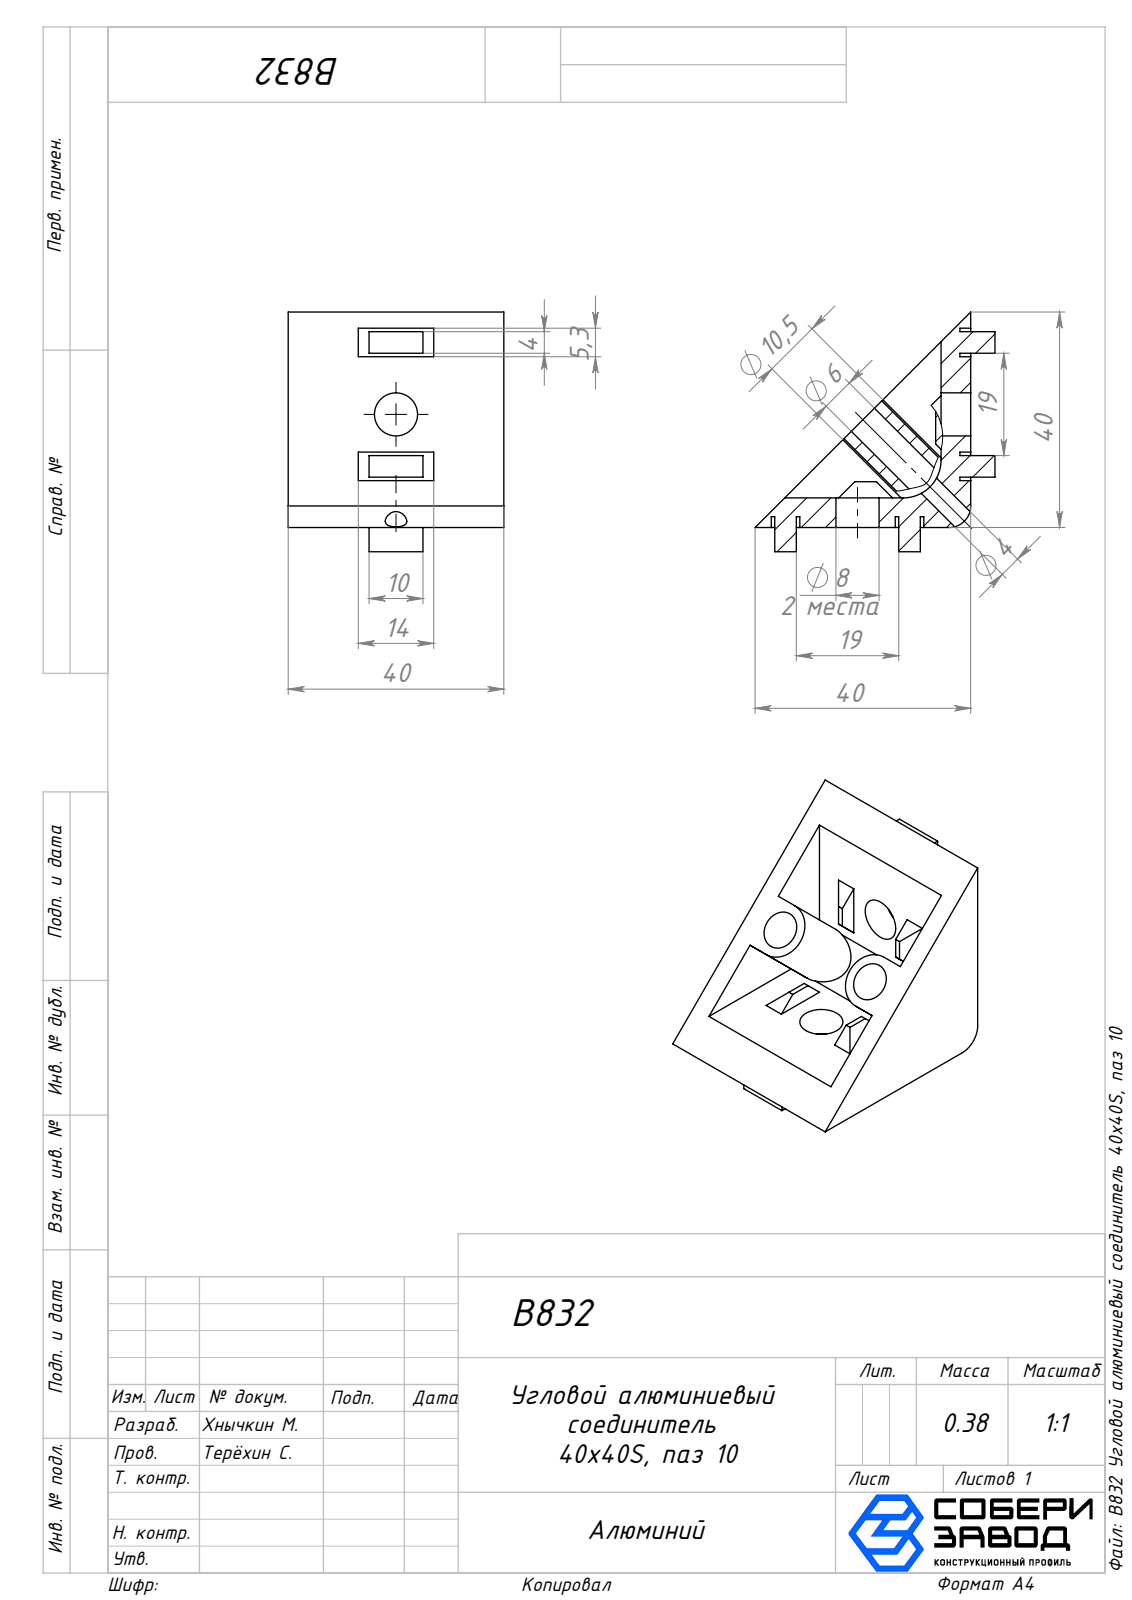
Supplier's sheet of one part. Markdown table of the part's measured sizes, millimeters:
| quantity | value |
| --- | --- |
| part name | B832 Угловой алюминиевый соединитель 40х40S, паз 10 |
| STEP written by | SolidWorks 2025 (AUTOMOTIVE_DESIGN) |
| units | millimeters |
| bodies | 1 solid, 91 faces (75 planar, 16 cylindrical, 0 other) |
| overall size | 44.5 × 44.5 × 40 |
| volume | 20 399 mm³ |
| surface area | 10 783 mm² |
| round holes (diameter × count) | 7 × 2, 8 × 2, 4 × 1 |
| partial cylindrical surfaces (radius × count) | 5.25 × 2, 4 × 1, 7 × 1 |
| main face-to-face distances | 5.5, 40, 4, 36, 22, 2, 10, 15, 13, 32 |
| hole center spacings | 11.75, 23.5 |
